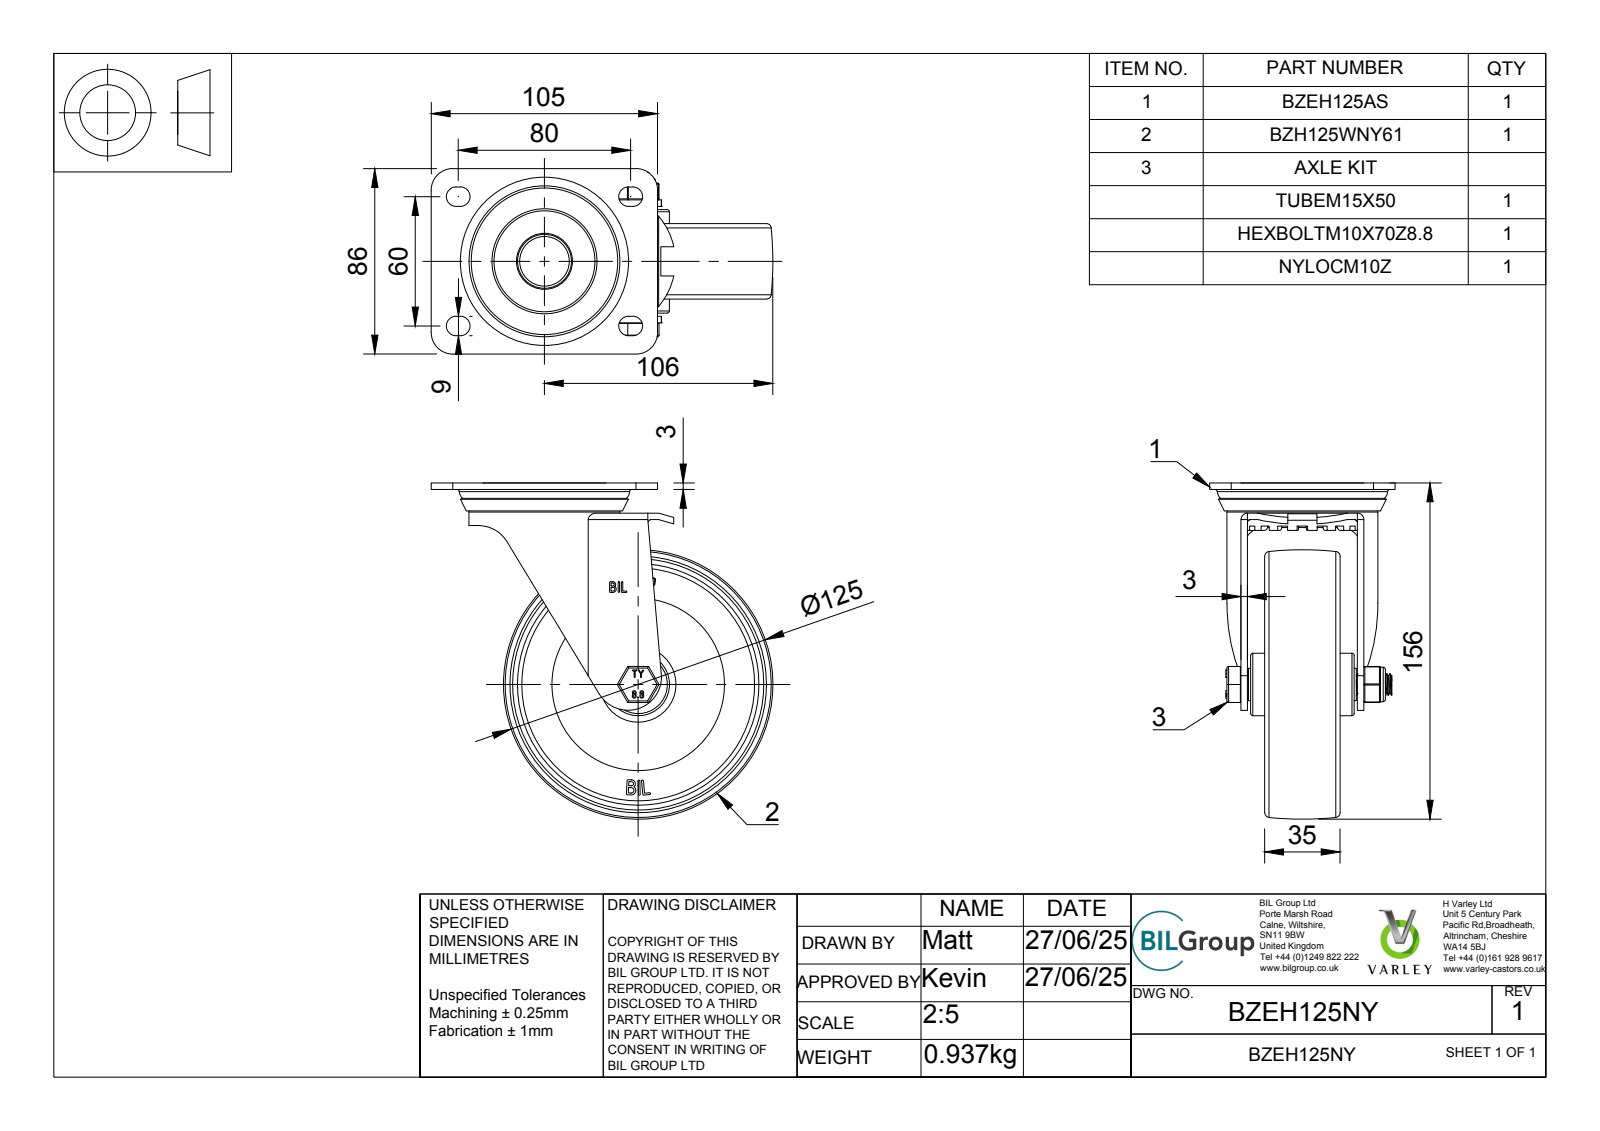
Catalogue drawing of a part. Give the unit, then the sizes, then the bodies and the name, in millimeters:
Units: millimetres
Overall size (bounding box): 158.5 × 156 × 86
Round holes (diameter × count): ⌀10 ×1, ⌀10.25 ×1, ⌀10.5 ×1, ⌀12 ×1, ⌀15.1 ×1, ⌀34 ×1, ⌀44.58 ×1, ⌀64 ×1, ⌀112 ×1
Round bosses / shafts (diameter × count): ⌀16 ×2, ⌀70 ×1, ⌀54 ×1, ⌀29 ×1, ⌀25 ×1, ⌀21 ×1, ⌀15 ×1, ⌀10 ×1
Partial cylindrical surfaces — rounded edges, fillets, slot ends (radius × count): R0.5 ×18, R4.5 ×8, R0.75 ×6, R1.5 ×4, R10 ×4, R3 ×2, R31.61 ×2, R15 ×1
Main face-to-face distances: 3, 7, 32, 25, 22, 29, 54, 14, 8, 6.5
Volume: 288 218 mm³ · Surface area: 121 824 mm²
Bodies: 28 solids, 631 faces (322 planar, 119 cylindrical, 190 other)
Part name (STEP PRODUCT): BZEH125NY v4; BZEH125AS - 2 v1; ZINC PLATED, PRESSED STEEL TOP PLATE; ZINC PLATED, PRESSED STEEL TOP PLATE Geometry (+7 more)
STEP written by: Autodesk Translation Framework v14.10.0.0 (AUTOMOTIVE_DESIGN)
